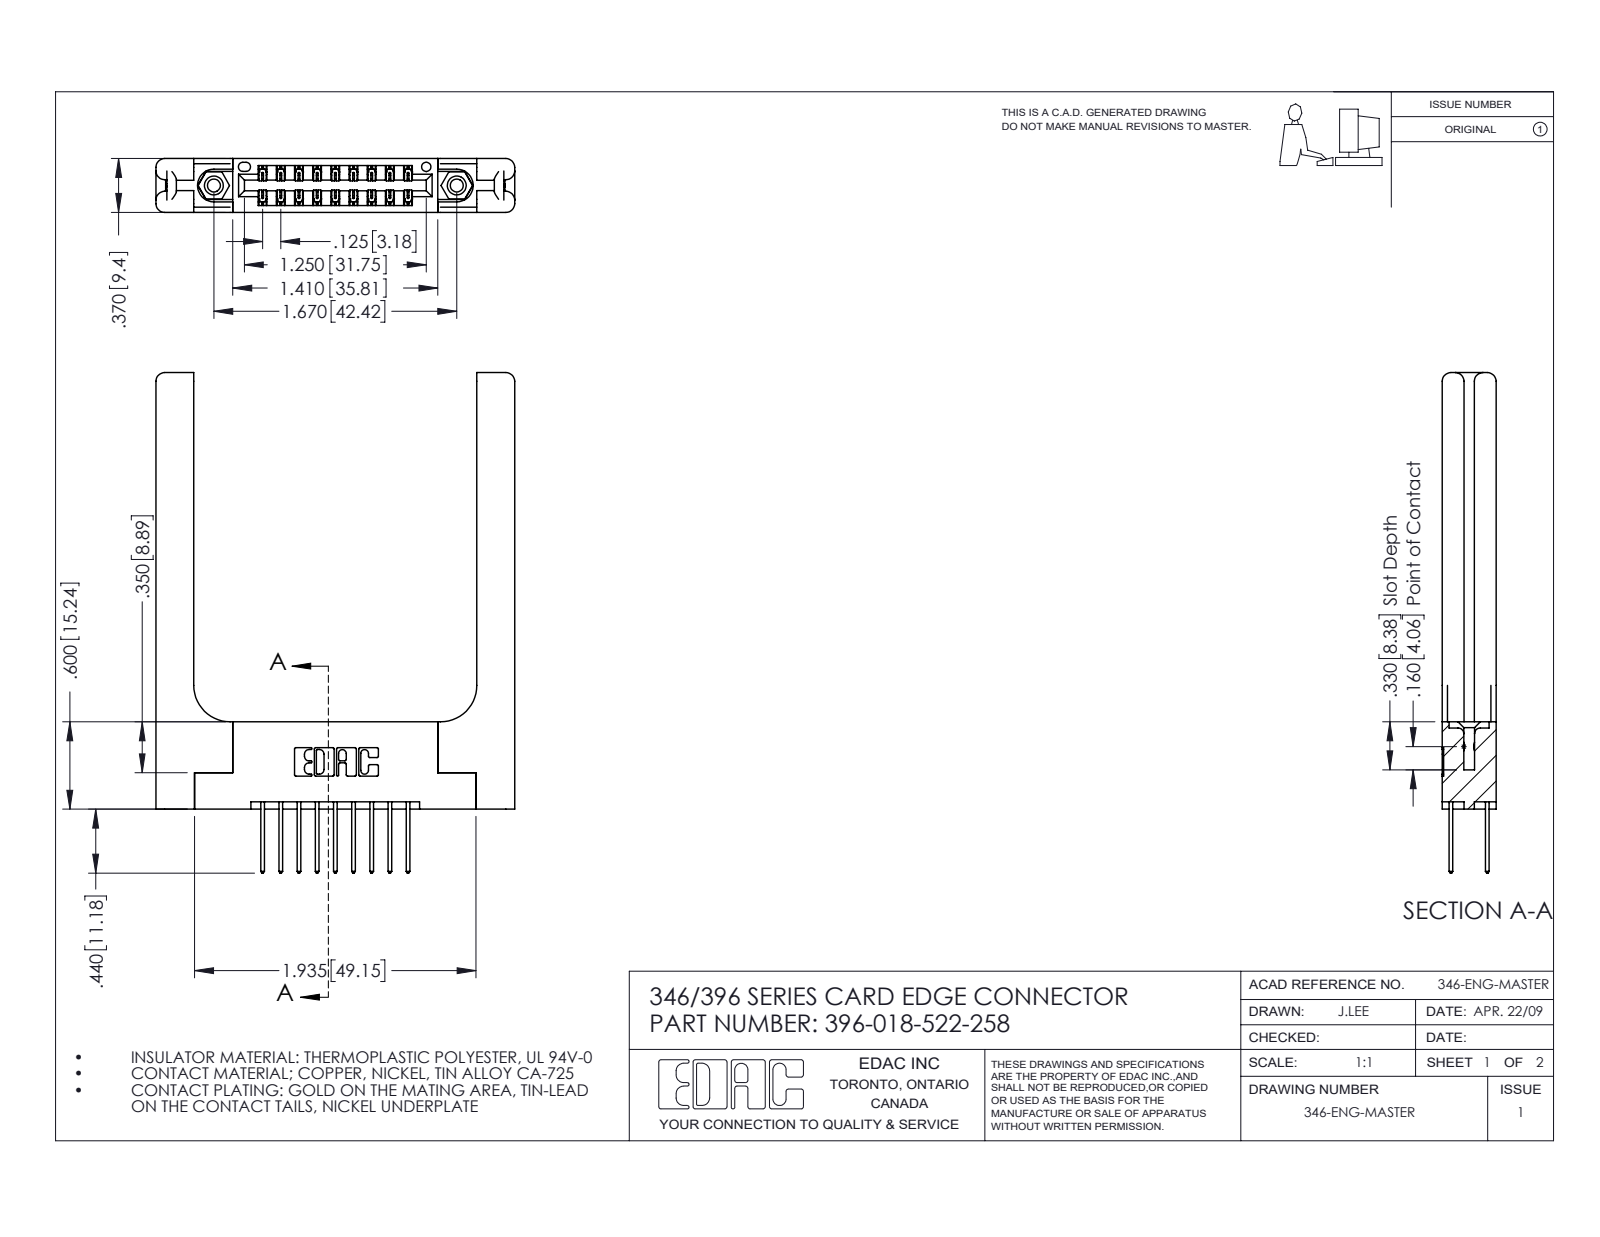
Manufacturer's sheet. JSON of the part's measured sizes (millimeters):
{"part_name": "346-220-058_345-220-058; 345-250-001_345-250-001-102; 345-292-001_345-293-122; 346 Part_Flush Mounting Lugs - 0.156 Dia-TH (+1 more)", "step_written_by": "SolidWorks 2016 (CONFIG_CONTROL_DESIGN)", "units": "millimeters", "bodies": {"solids": 23, "faces": 1314, "planar": 854, "cylindrical": 400, "other": 60}, "overall_size": [87.4, 62.6, 9.4], "volume_mm3": 13400, "surface_area_mm2": 12770, "round_holes": [[2.3, 2], [3.2, 2], [4, 2], [1.6, 1]], "round_bosses_or_shafts": [[3.9, 2]], "partial_cylinders_radius": [[0.2, 27], [0.3, 22], [0.3, 18], [1.5, 16], [0.2, 6], [0.8, 6], [0.7, 3], [0.4, 2]], "face_to_face_distances": [9.4, 3.8, 1.8, 3.8, 6.4, 5.6, 2.6, 1.2, 8.2, 4.4], "hole_center_spacings": [6.2, 37.2, 42.4]}
